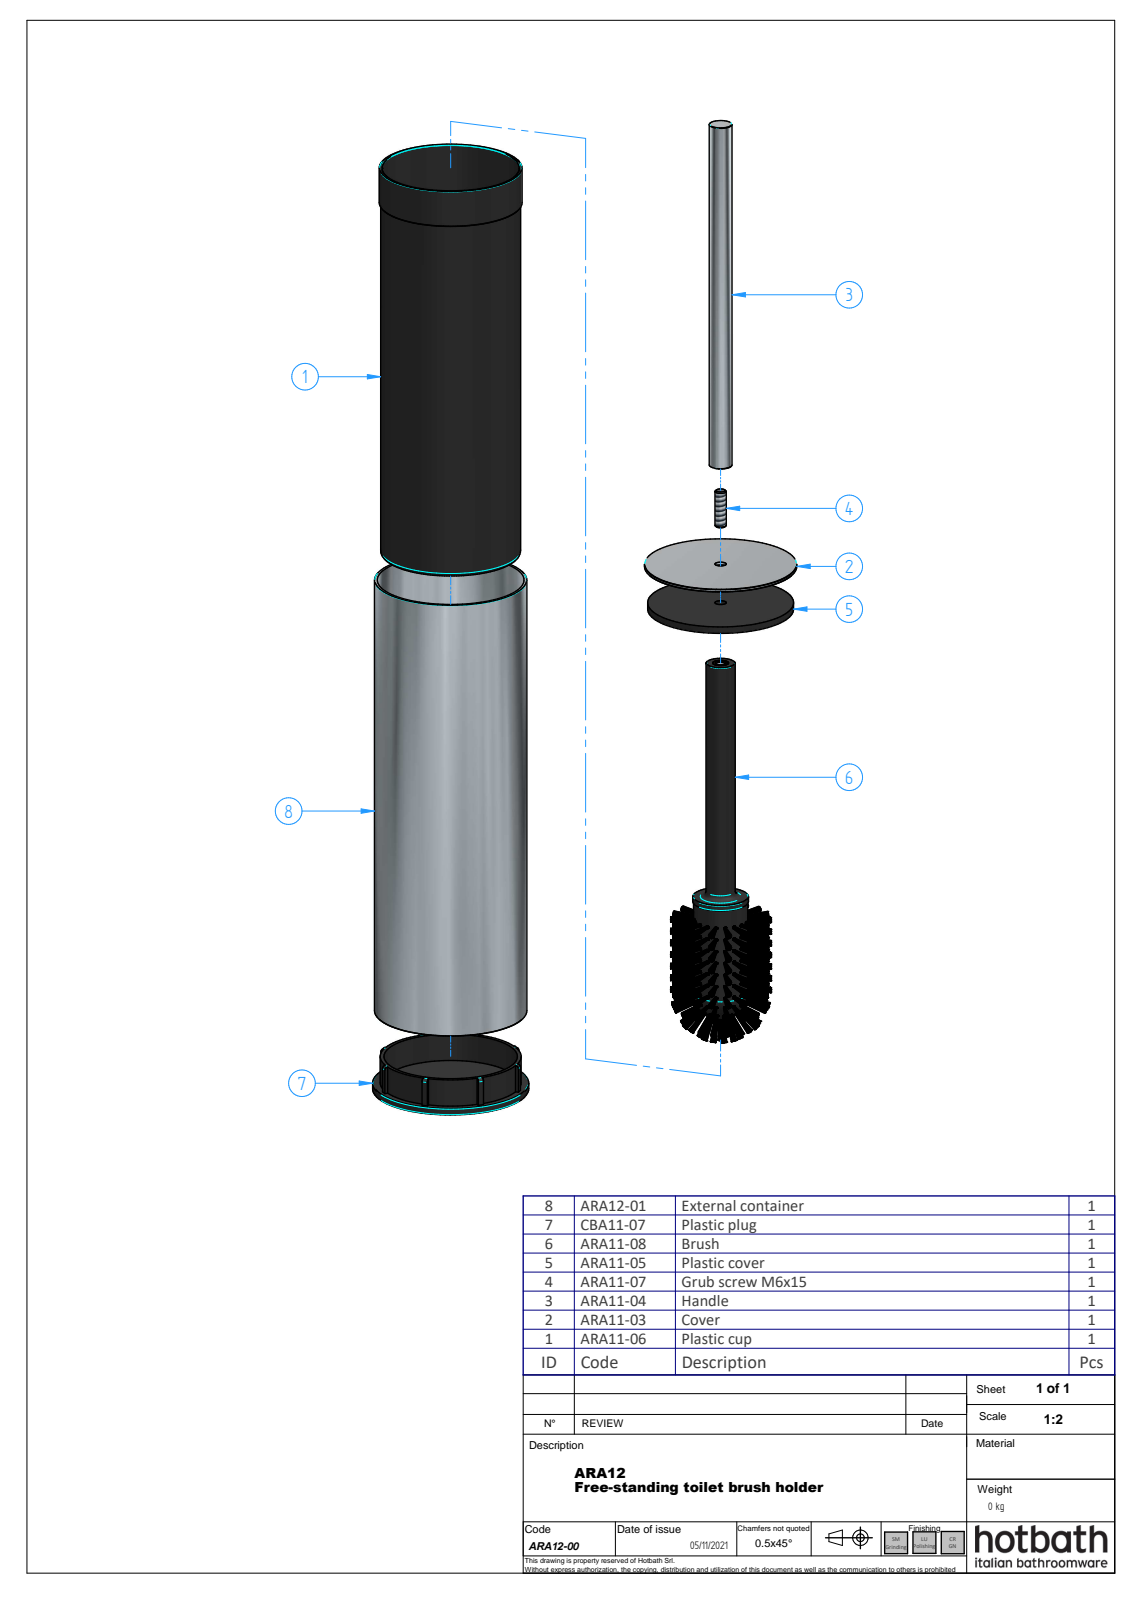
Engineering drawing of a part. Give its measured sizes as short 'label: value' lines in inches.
name: ARA12-00; CBA11-07; ARA12-01; ARA11-03 (+1 more)
written by: ST-DEVELOPER v16.7 (AP242_MANAGED_MODEL_BASED_3D_ENGINEERING_MIM_LF)
unit: in
bodies: 4 solids, 71 faces (27 planar, 25 cylindrical, 19 other)
size: 17.13 × 3.228 × 3.228
volume: 8.591 in³; area: 241 in²
holes: 1× ⌀0.194, 1× ⌀0.236, 1× ⌀2.756, 1× ⌀3.031
bosses: 1× ⌀3.228, 1× ⌀3.15, 1× ⌀2.913, 1× ⌀0.472
rounds: 1× R1.52
face distances: 9.449, 9.508, 0.059, 0.102, 9.551, 9.61, 0.039, 0.142, 9.591, 9.65
